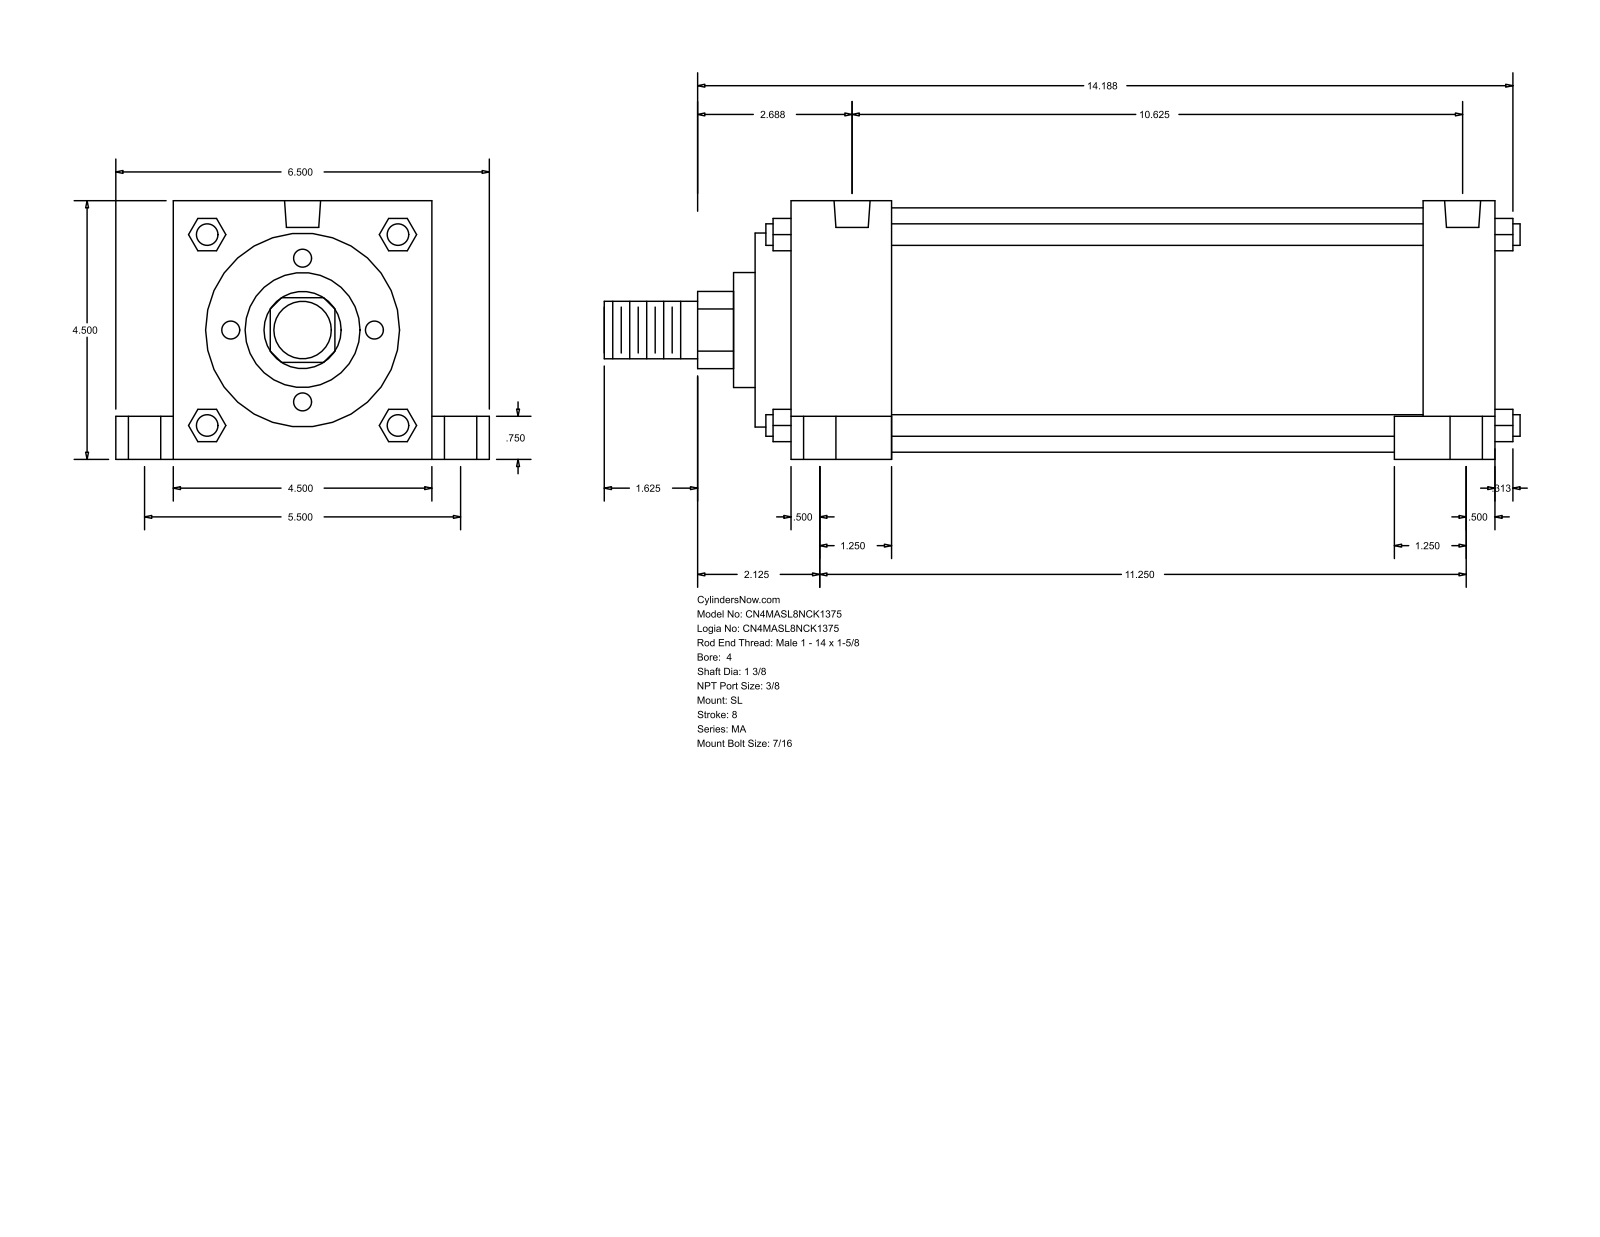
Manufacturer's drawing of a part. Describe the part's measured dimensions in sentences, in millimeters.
The part is named "MA_SL__0400_1.375". Its 3-D file was written by "GSSL Pune (CONFIG_CONTROL_DESIGN)". It is 0 solids with 150 faces: 113 planar, 37 cylindrical and 0 other. Overall it measures 404.81 by 165.1 by 114.3 millimeters. Round holes: 4 of diameter 11.11, 4 of diameter 14.29, 4 of diameter 20.64, 2 of diameter 15.93. Round bosses or shafts: 4 of diameter 9.53, 1 of diameter 107.95, 1 of diameter 85.72, 1 of diameter 50.8, 1 of diameter 34.92, 1 of diameter 25.4. Partial cylindrical surfaces (rounded edges, fillets, slot ends): 1 of radius 17.06. The main face-to-face distances are 114.3, 311.16, 15.87, 327.03, 60.32, 44.45, 266.71, 295.28, 279.41, 234.96. The hole center spacings are 69.87, 70.14, 71.29, 72.4, 139.7, 260.35, 275.7, 280.31.
